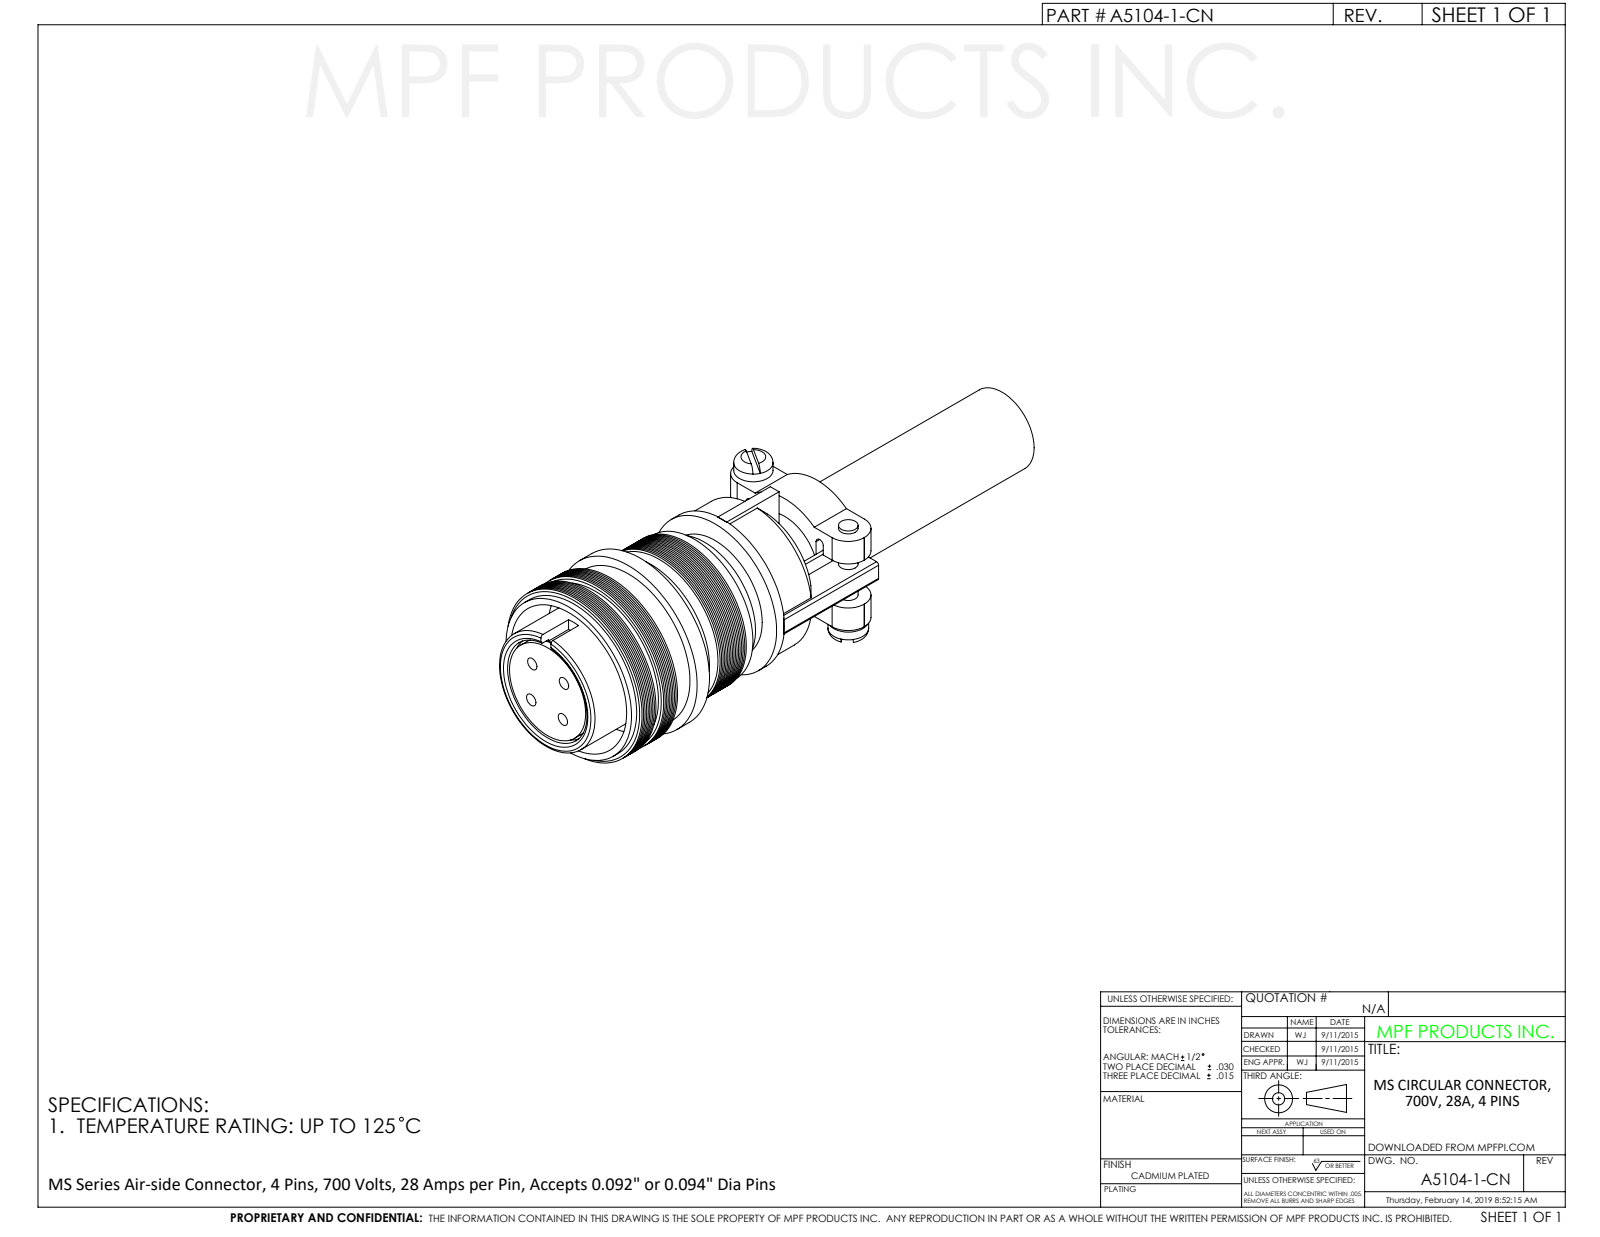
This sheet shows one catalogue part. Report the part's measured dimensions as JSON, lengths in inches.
{"part_name": "A5104-1-CN", "step_written_by": "SolidWorks 2012 (CONFIG_CONTROL_DESIGN)", "units": "inches", "bodies": {"solids": 1, "faces": 376, "planar": 107, "cylindrical": 87, "other": 182}, "overall_size": [4.437, 1.34, 1.34], "volume_in3": 2.391, "surface_area_in2": 31.49, "round_holes": [[0.091, 4], [0.55, 1], [0.78, 1], [1.125, 1]], "round_bosses_or_shafts": [[0.135, 2], [1.34, 1], [1.223, 1], [1.22, 1], [1.2, 1], [1.14, 1], [0.99, 1], [0.92, 1]], "partial_cylinders_radius": [[0.034, 8], [0.02, 4], [0.156, 4], [0.323, 1], [0.472, 1], [0.473, 1]], "face_to_face_distances": [1.193, 0.643, 0.47, 0.722, 0.1, 0.2, 2.096, 1.626, 0.904, 0.522], "hole_center_spacings": [0.218, 0.308, 0.436]}
